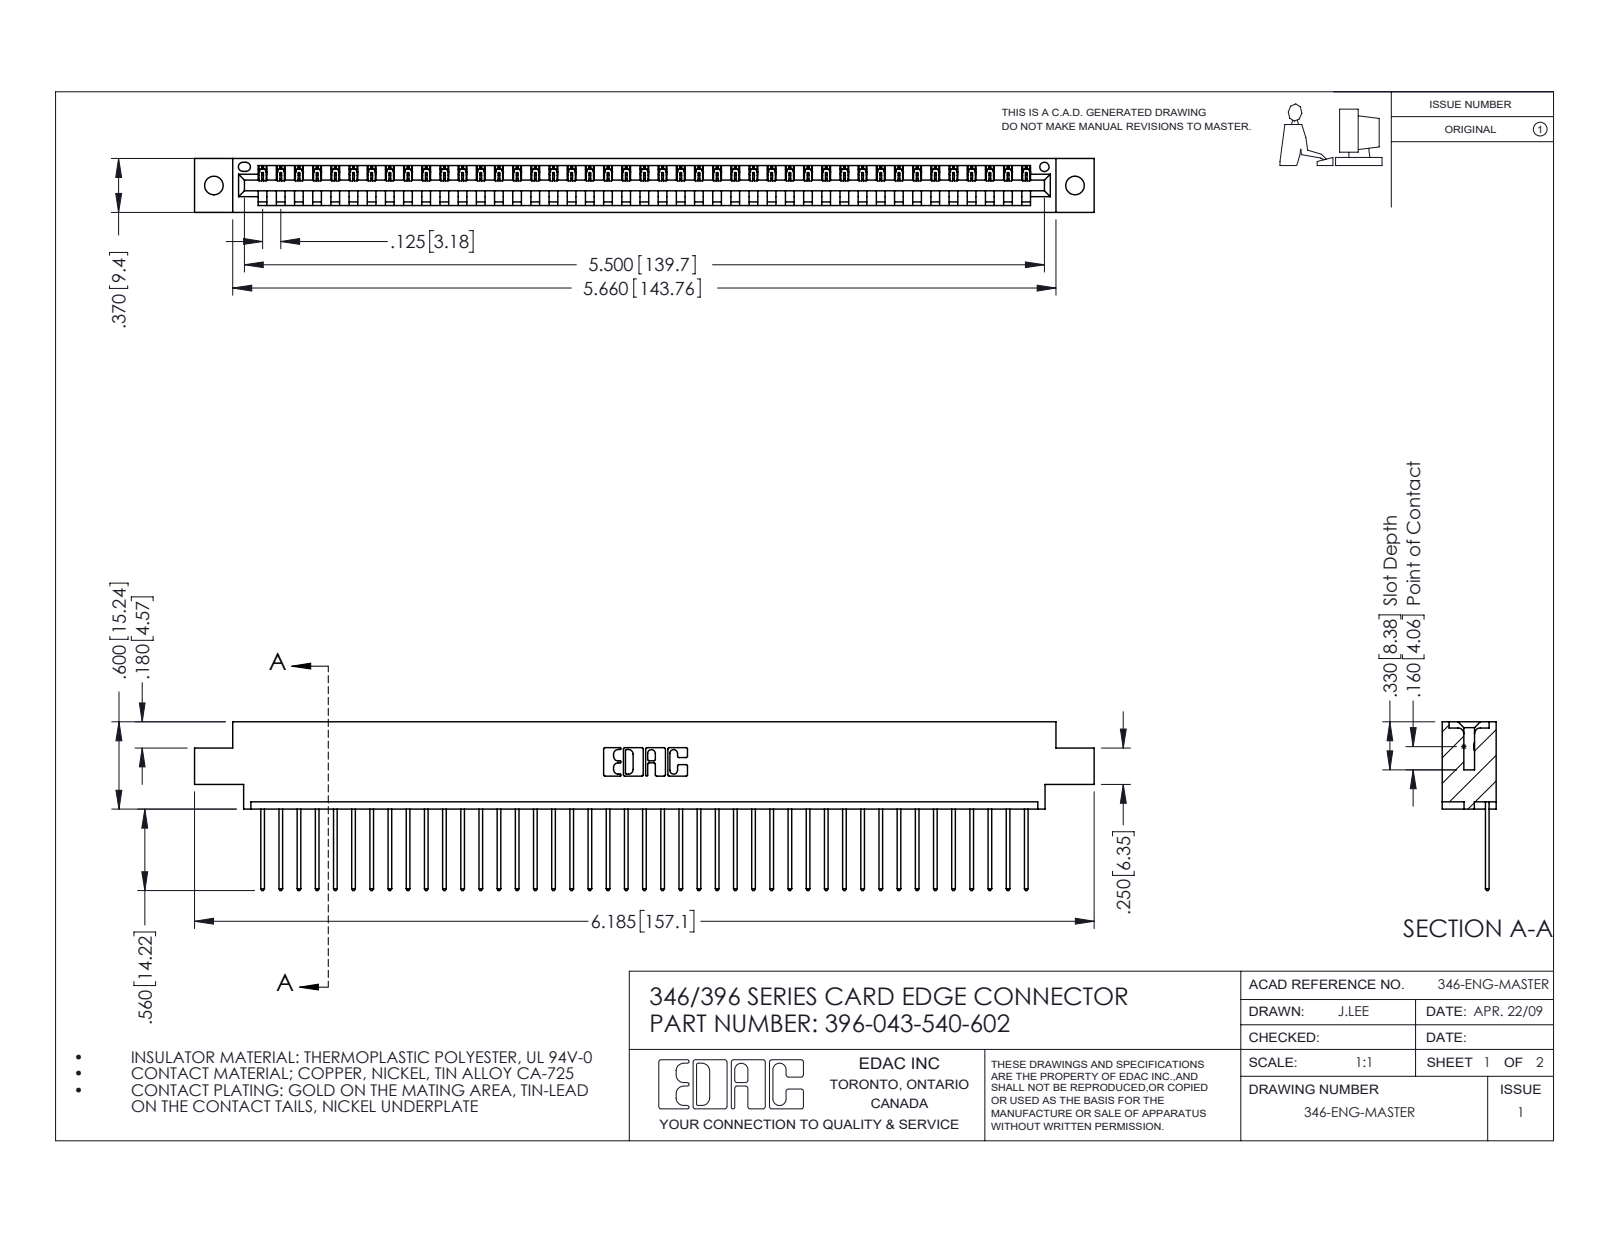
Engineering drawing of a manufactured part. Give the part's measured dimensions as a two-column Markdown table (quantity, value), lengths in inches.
| quantity | value |
| --- | --- |
| part name | 396-043-540-602; 345-292-001_345-293-140; 346 Part_0.170 Offset - 0.128 Dia |
| STEP written by | SolidWorks 2016 (CONFIG_CONTROL_DESIGN) |
| units | inches |
| bodies | 44 solids, 2620 faces (1800 planar, 820 cylindrical, 0 other) |
| overall size | 6.185 × 1.16 × 0.37 |
| volume | 0.91 in³ |
| surface area | 29.39 in² |
| round holes (diameter × count) | 0.128 × 2, 0.064 × 1 |
| partial cylindrical surfaces (radius × count) | 0.006 × 86, 0.01 × 86, 0.01 × 22, 0.007 × 6, 0.031 × 6, 0.026 × 3, 0.031 × 2, 0.04 × 2 |
| main face-to-face distances | 0.048, 0.322, 0.37, 0.25, 0.072, 0.298, 0.025, 0.148, 0.222, 0.1 |
| hole center spacings | 0.246, 5.711, 5.92 |
